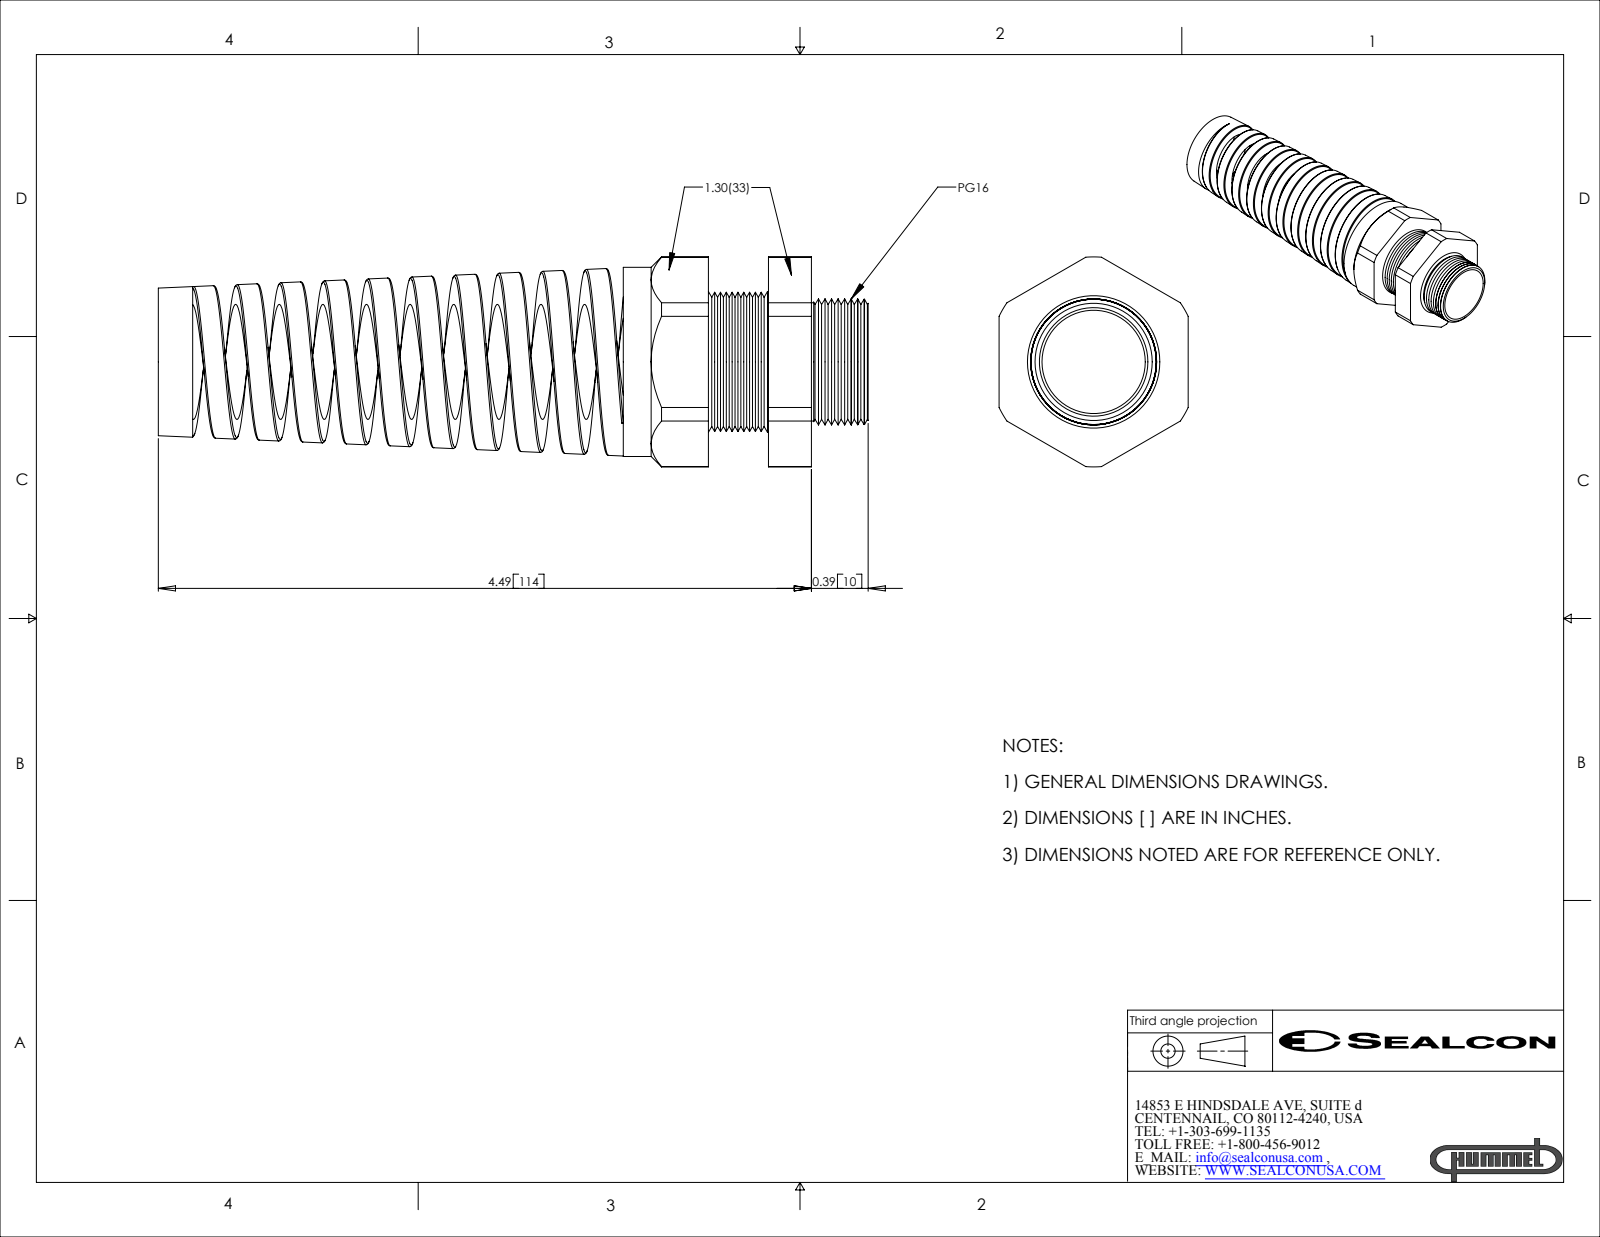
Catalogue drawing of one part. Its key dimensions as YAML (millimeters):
part_name: "CF16GR-BK"
step_written_by: "SolidWorks 2007 (CONFIG_CONTROL_DESIGN)"
units: millimeters
bodies: {solids: 2, faces: 193, planar: 24, cylindrical: 45, other: 124}
overall_size: [124, 36.7, 33]
volume: 32810
surface_area: 25850
round_holes:
  - {diameter: 18, count: 1}
  - {diameter: 20.1, count: 1}
round_bosses_or_shafts:
  - {diameter: 33, count: 1}
  - {diameter: 24.6, count: 1}
partial_cylinders:
  - {radius: 10.3, count: 1}
  - {radius: 18.3, count: 1}
face_to_face_distances: [33, 18, 10.5, 7.5, 14.9, 25.3, 32.9, 81.2, 96.1, 106.6]
